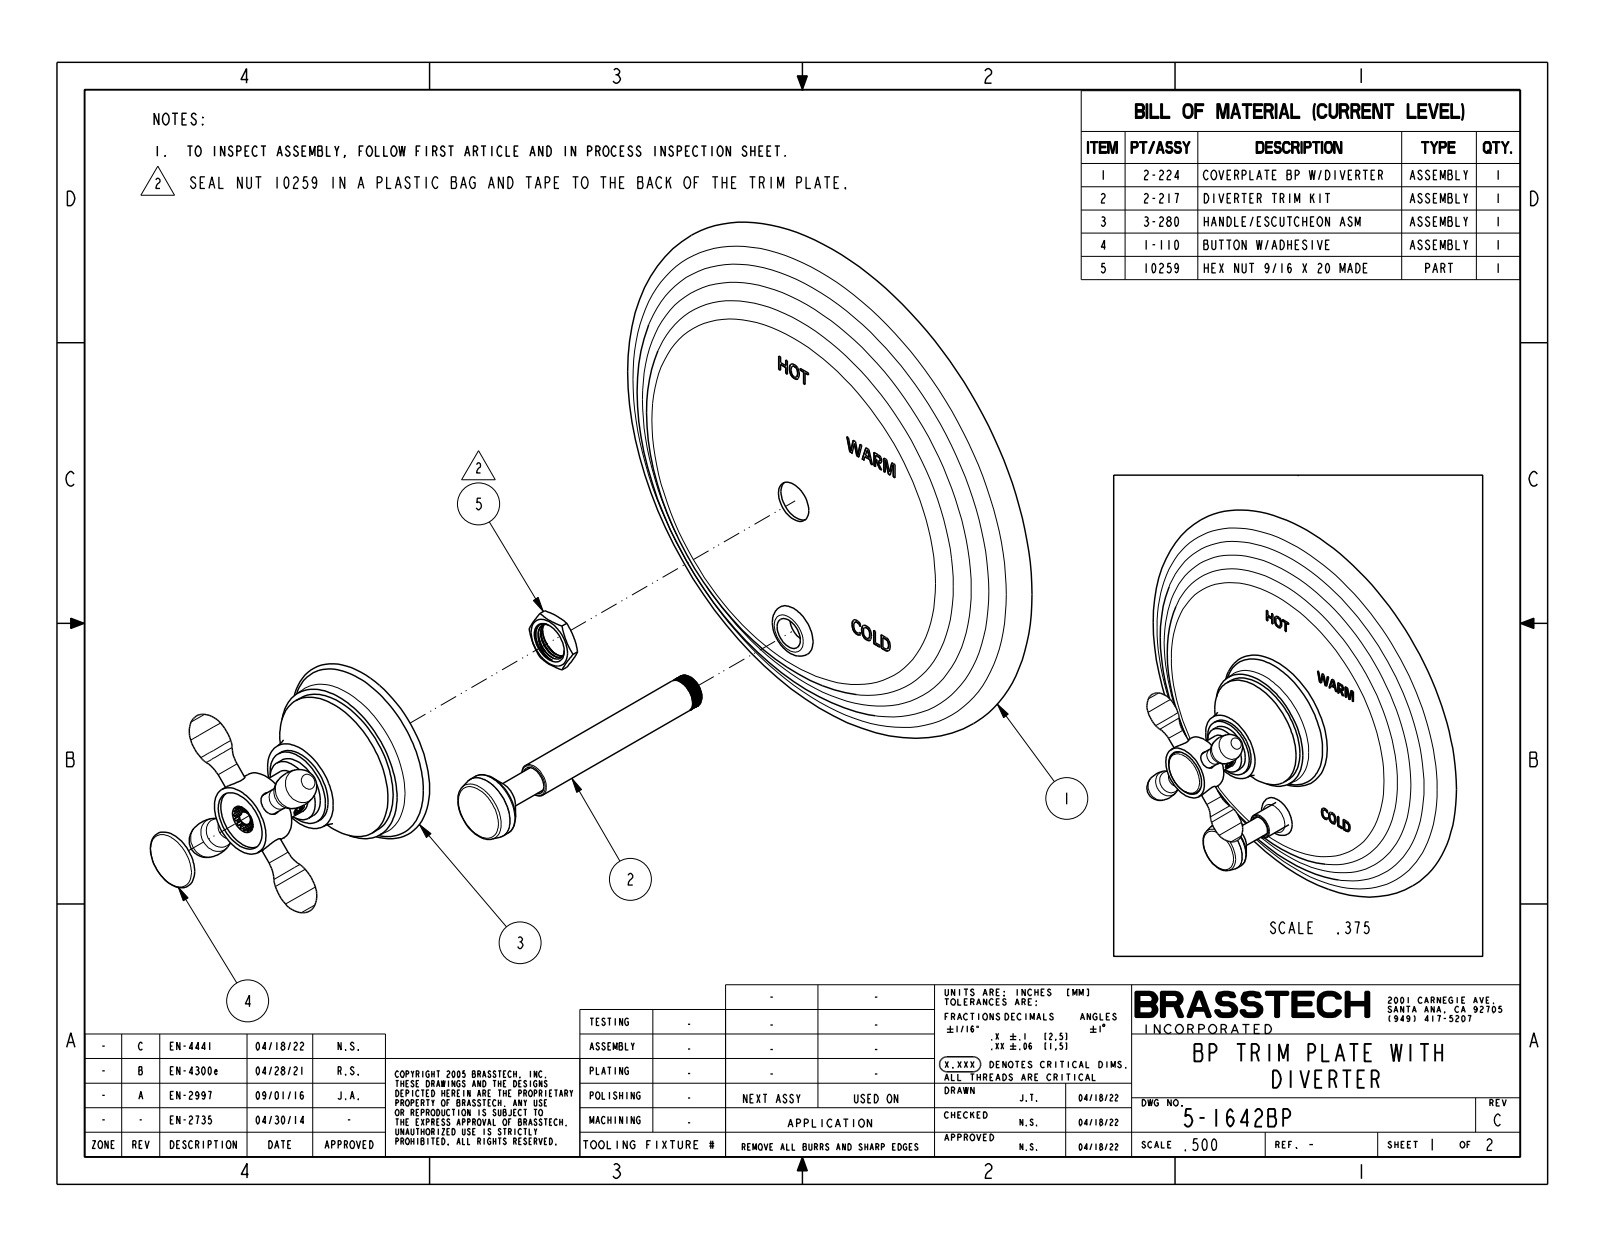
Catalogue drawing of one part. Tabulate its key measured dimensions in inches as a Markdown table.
| quantity | value |
| --- | --- |
| part name | 5-1642BP |
| STEP written by | CREO PARAMETRIC BY PTC INC, 2018400 (CONFIG_CONTROL_DESIGN) |
| units | inches |
| bodies | 1 solid, 292 faces (114 planar, 36 cylindrical, 142 other) |
| overall size | 7.75 × 7.75 × 3.224 |
| volume | 32.91 in³ |
| surface area | 120.2 in² |
| round holes (diameter × count) | 0.313 × 2, 0.85 × 1 |
| round bosses / shafts (diameter × count) | 0.3 × 2, 2.1 × 1, 1.075 × 1, 1 × 1, 0.9 × 1, 0.875 × 1, 0.625 × 1, 0.472 × 1 |
| main face-to-face distances | 0.754, 1.229, 0.475, 0.9, 2.129, 1.375, 0.157, 2.286, 1.532, 1.057 |
